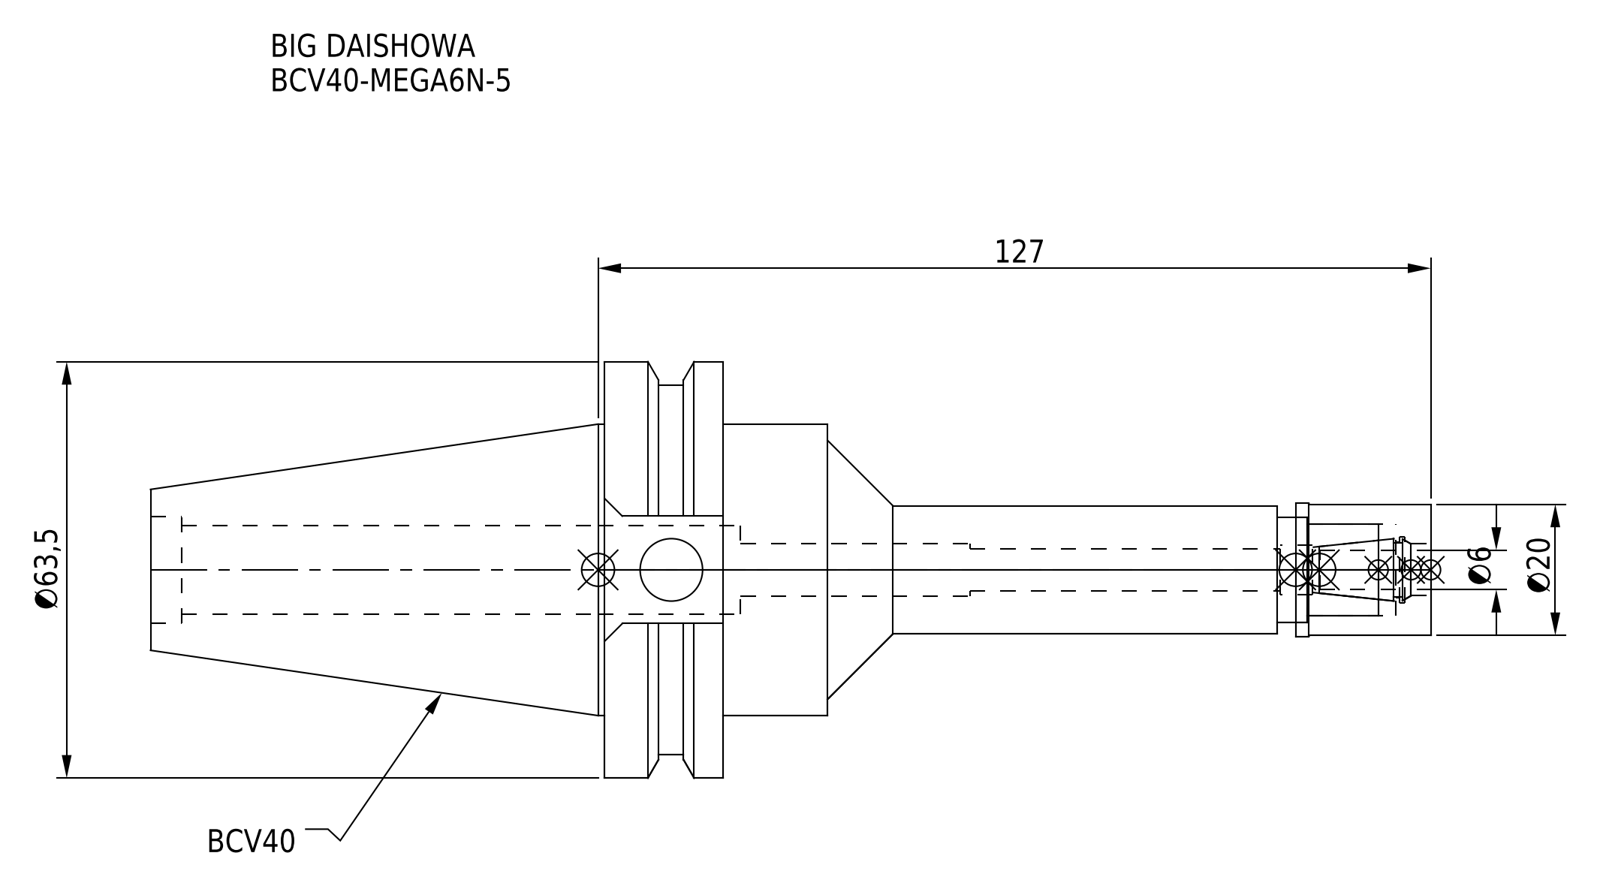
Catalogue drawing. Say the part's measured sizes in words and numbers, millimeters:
The part is named "BCV40-MEGA6N-5-060.stp; BCV40MN06050-060_ASM.stp; BCV40-MEGA6N-5; BCV40-MEGA6N-5-060-FreeParts (+3 more)". Its 3-D file was written by "SolidWorks 2019 (CONFIG_CONTROL_DESIGN)". It is 2 solids with 91 faces: 33 planar, 44 cylindrical and 14 other. Overall it measures 195.25 by 63.5 by 61.35 millimeters. Its volume is 155 115 cubic millimeters and its surface area 32 586 square millimeters. Round holes: 1 of diameter 6.4, 1 of diameter 7.5, 1 of diameter 7.9, 1 of diameter 8, 1 of diameter 8.5, 1 of diameter 9.53, 1 of diameter 10, 1 of diameter 13.6, 1 of diameter 14, 1 of diameter 16, 1 of diameter 16.32. Round bosses or shafts: 1 of diameter 63.5, 1 of diameter 56.36, 1 of diameter 44.45, 1 of diameter 20.3, 1 of diameter 20, 1 of diameter 19.5. The main face-to-face distances are 18.05, 15.95, 34, 92, 107.95, 126, 195.25, 103.25, 87.3, 69.25.
